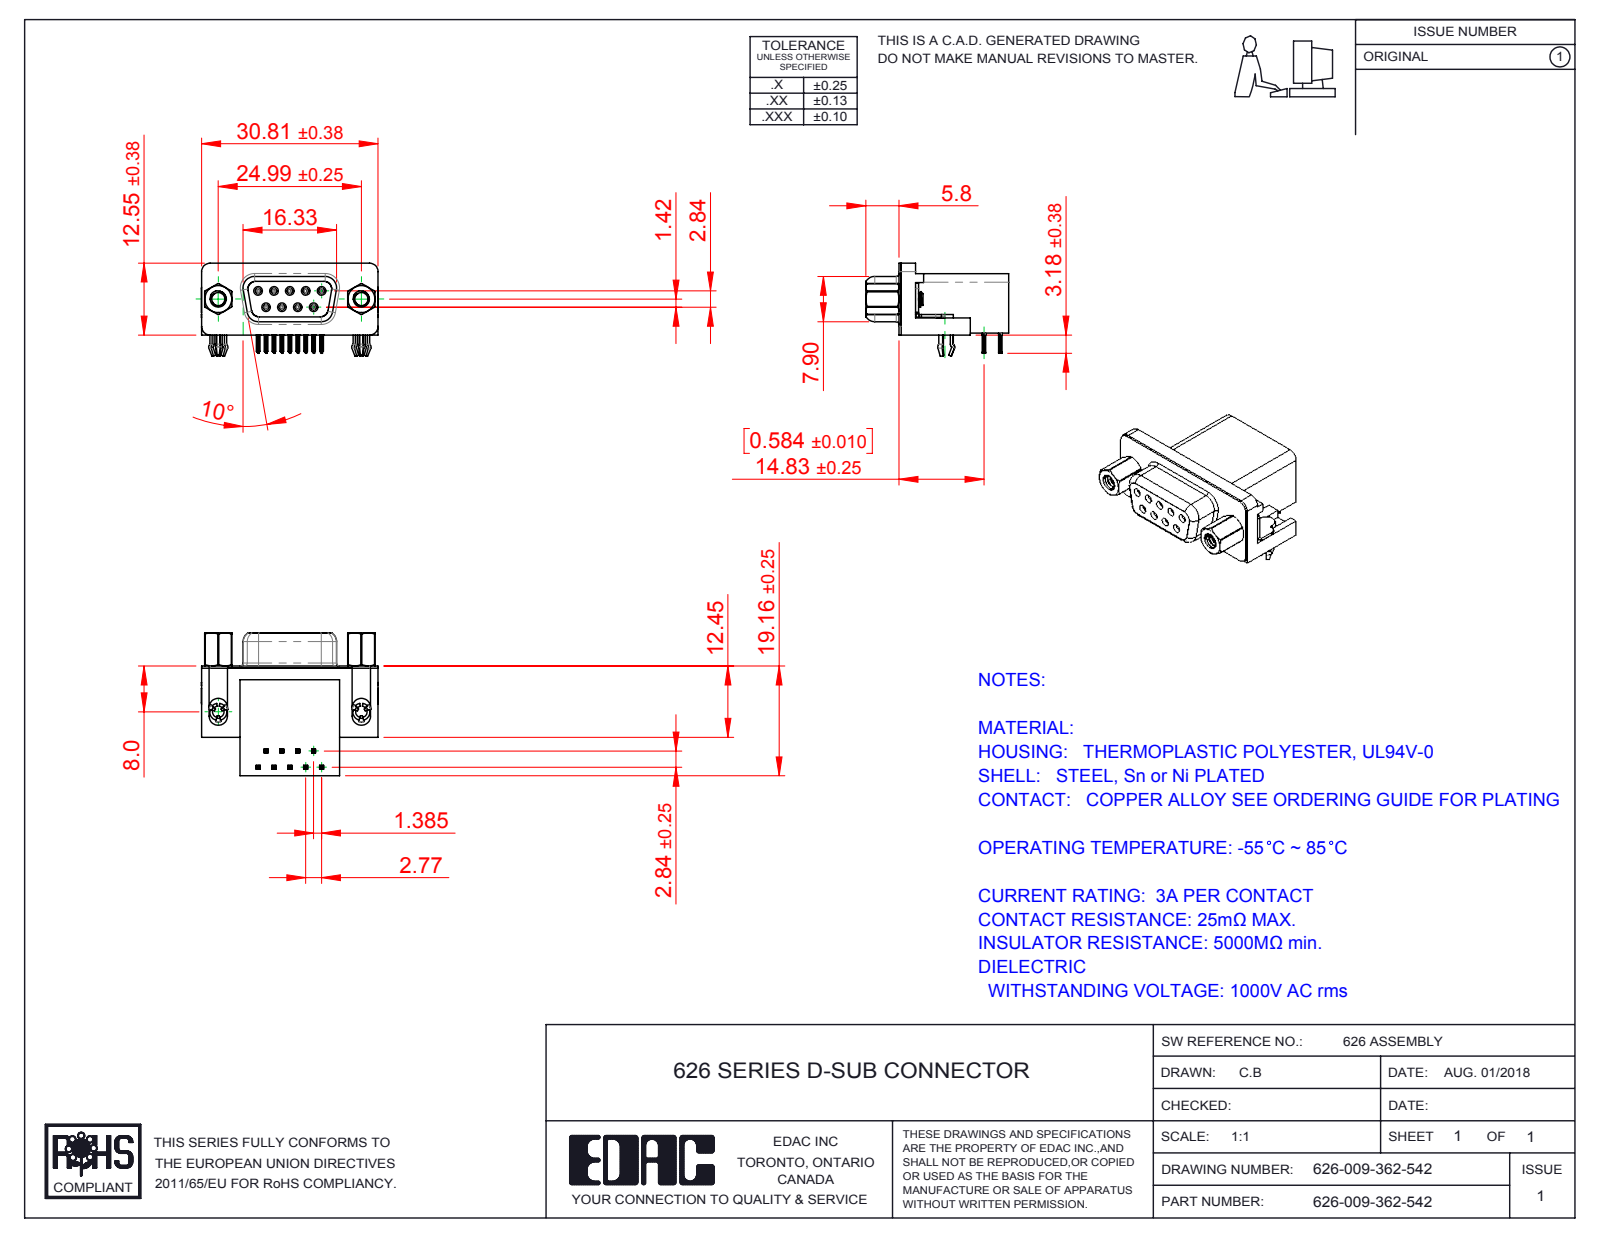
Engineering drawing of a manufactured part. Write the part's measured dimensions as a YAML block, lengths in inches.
part_name: "626-009-362-542; 626 4-40 Hex Standoff 5; 626 Housing_9 Socket; 626 3 Prong Board Lock (+3 more)"
step_written_by: "SolidWorks 2016 (CONFIG_CONTROL_DESIGN)"
units: inches
bodies: {solids: 15, faces: 1714, planar: 728, cylindrical: 456, other: 530}
overall_size: [1.216, 0.983, 0.64]
volume: 0.312
surface_area: 9.322
round_holes:
  - {diameter: 0.031, count: 9}
  - {diameter: 0.035, count: 9}
  - {diameter: 0.079, count: 2}
  - {diameter: 0.09, count: 2}
  - {diameter: 0.157, count: 2}
  - {diameter: 0.189, count: 2}
  - {diameter: 0.197, count: 2}
round_bosses_or_shafts:
  - {diameter: 0.047, count: 9}
  - {diameter: 0.193, count: 2}
  - {diameter: 0.118, count: 2}
  - {diameter: 0.11, count: 2}
partial_cylinders:
  - {radius: 0.004, count: 72}
  - {radius: 0.006, count: 36}
  - {radius: 0.014, count: 18}
  - {radius: 0.039, count: 18}
  - {radius: 0.013, count: 9}
  - {radius: 0.053, count: 8}
  - {radius: 0.063, count: 8}
  - {radius: 0.059, count: 7}
face_to_face_distances: [0.016, 0.407, 0.014, 0.739, 0.754, 0.64, 0.114, 0.098, 0.244, 0.228]
hole_center_spacings: [0.124, 0.109, 0.218, 0.198, 0.198, 0.327, 0.294, 0.295]
